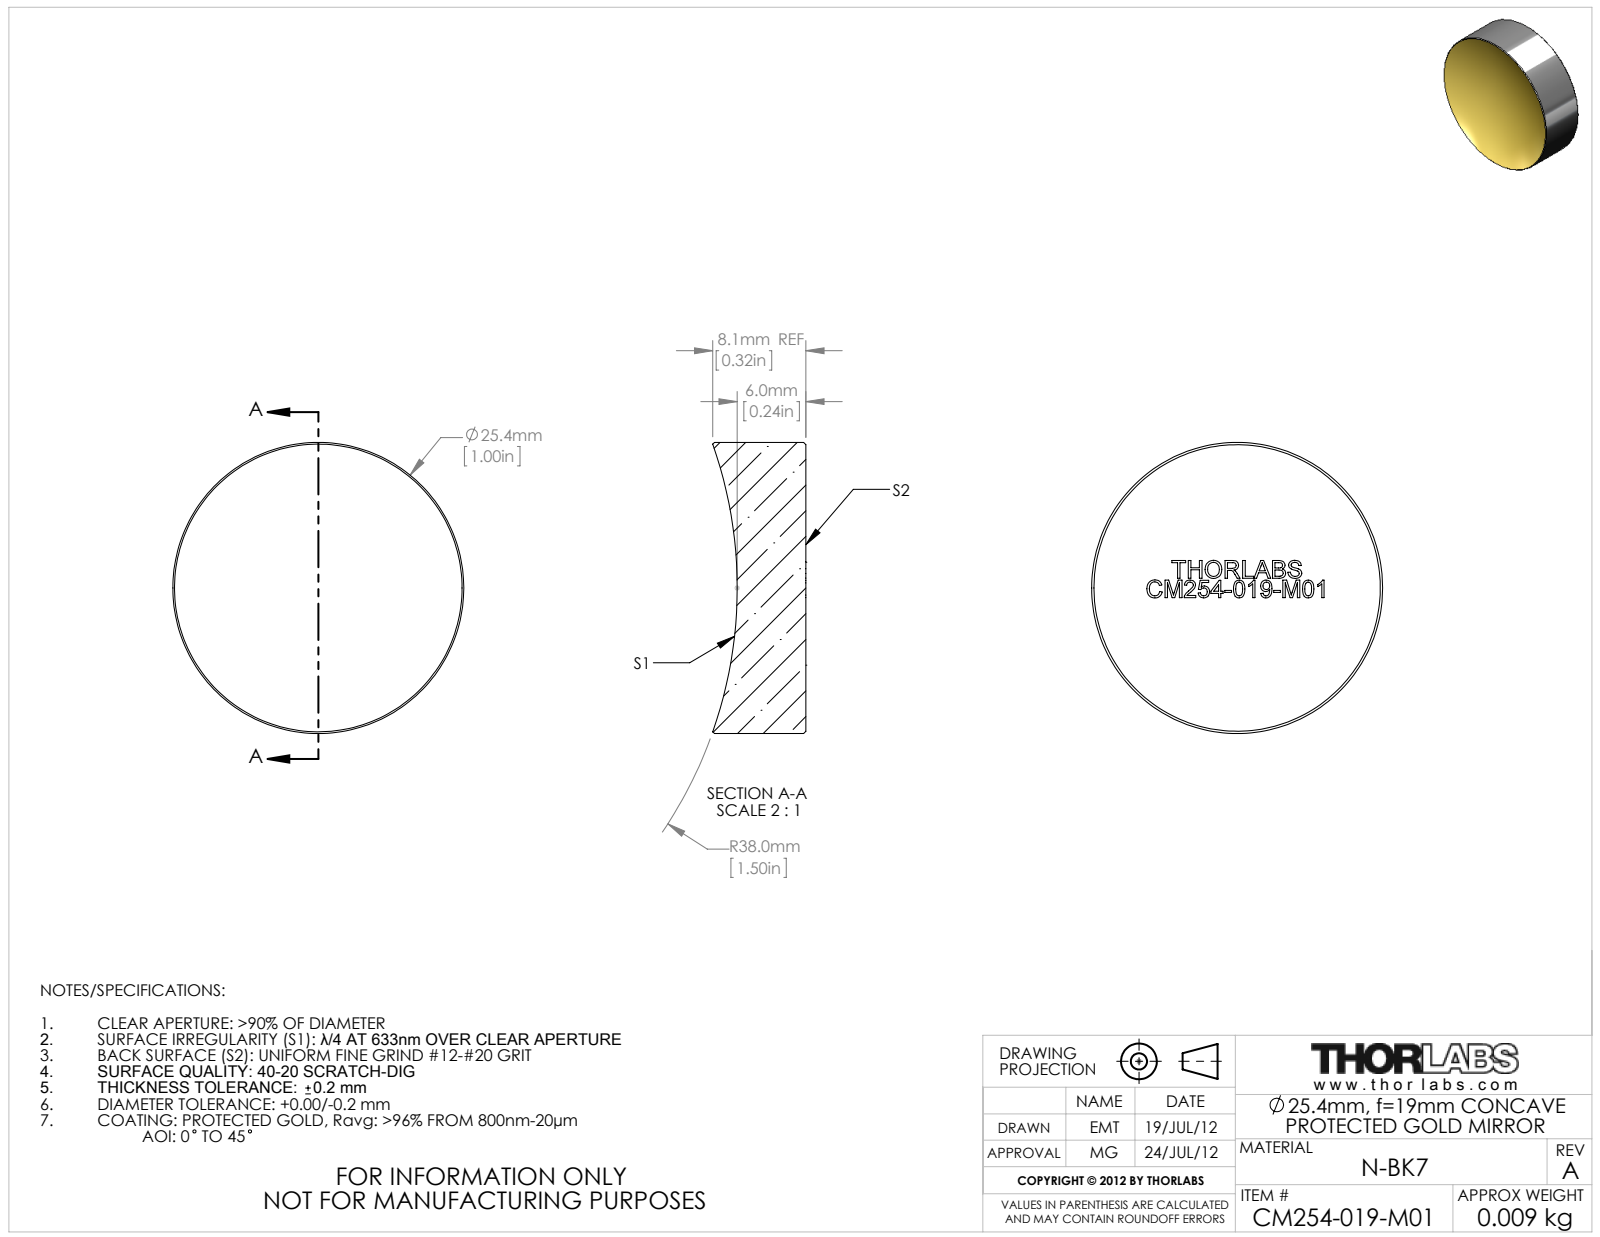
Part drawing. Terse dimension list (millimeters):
name: 24631-E0W
written by: SolidWorks 2011 (CONFIG_CONTROL_DESIGN)
unit: mm
bodies: 0 solids, 39 faces (31 planar, 2 cylindrical, 6 other)
size: 25.4 × 25.4 × 8.1
bosses: 1× ⌀25.4
